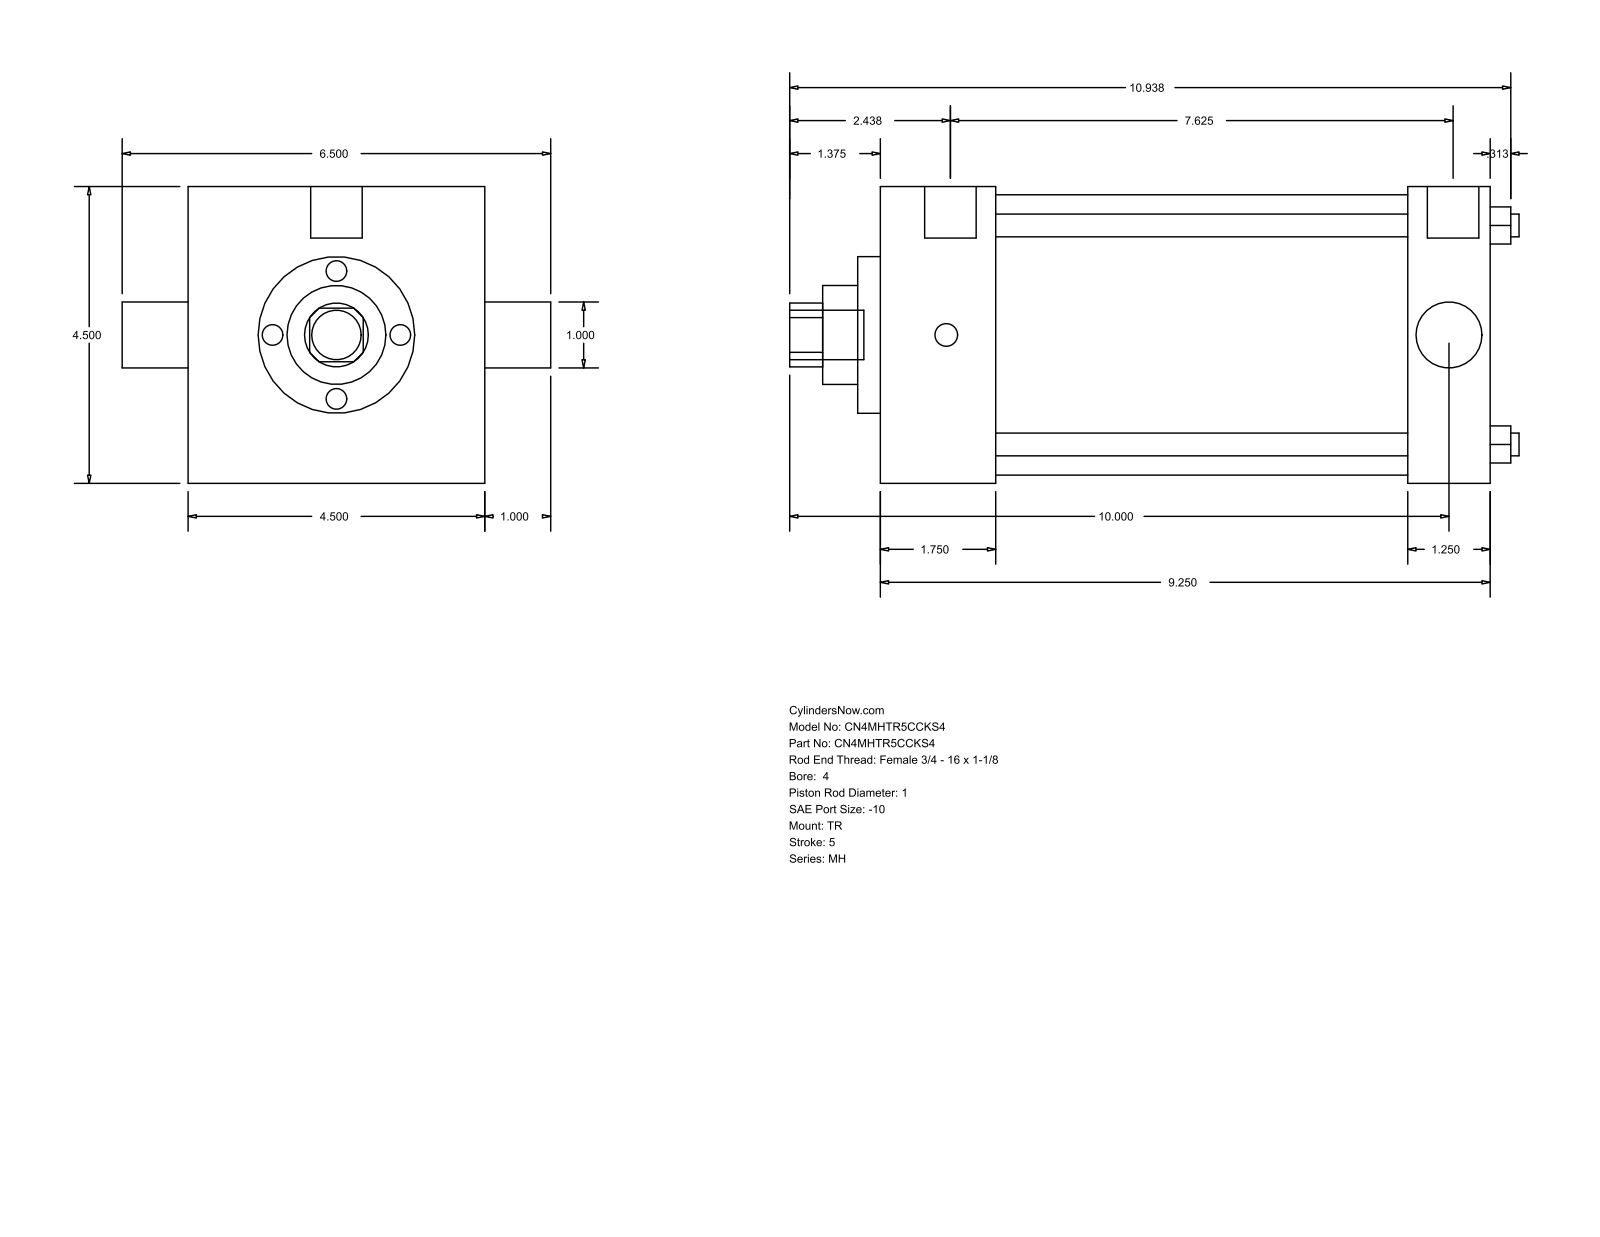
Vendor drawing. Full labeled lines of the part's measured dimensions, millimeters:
Part name (STEP PRODUCT): MH_TR__0400_1
STEP written by: GSSL Pune (CONFIG_CONTROL_DESIGN)
Units: millimetres
Bodies: 0 solids, 86 faces (61 planar, 25 cylindrical, 0 other)
Overall size (bounding box): 280.99 × 165.1 × 114.3
Round holes (diameter × count): ⌀8.76 ×4, ⌀25.4 ×2, ⌀38.1 ×1, ⌀60.33 ×1, ⌀107.95 ×1
Round bosses / shafts (diameter × count): ⌀8.73 ×3, ⌀19.84 ×2, ⌀19.05 ×1
Partial cylindrical surfaces — rounded edges, fillets, slot ends (radius × count): R12.29 ×1
Main face-to-face distances: 114.3, 234.96, 44.46, 190.5, 203.2, 158.74, 31.76, 8.73, 53.19, 211.93
Hole centre spacings: 59.62, 84.32, 119.25
